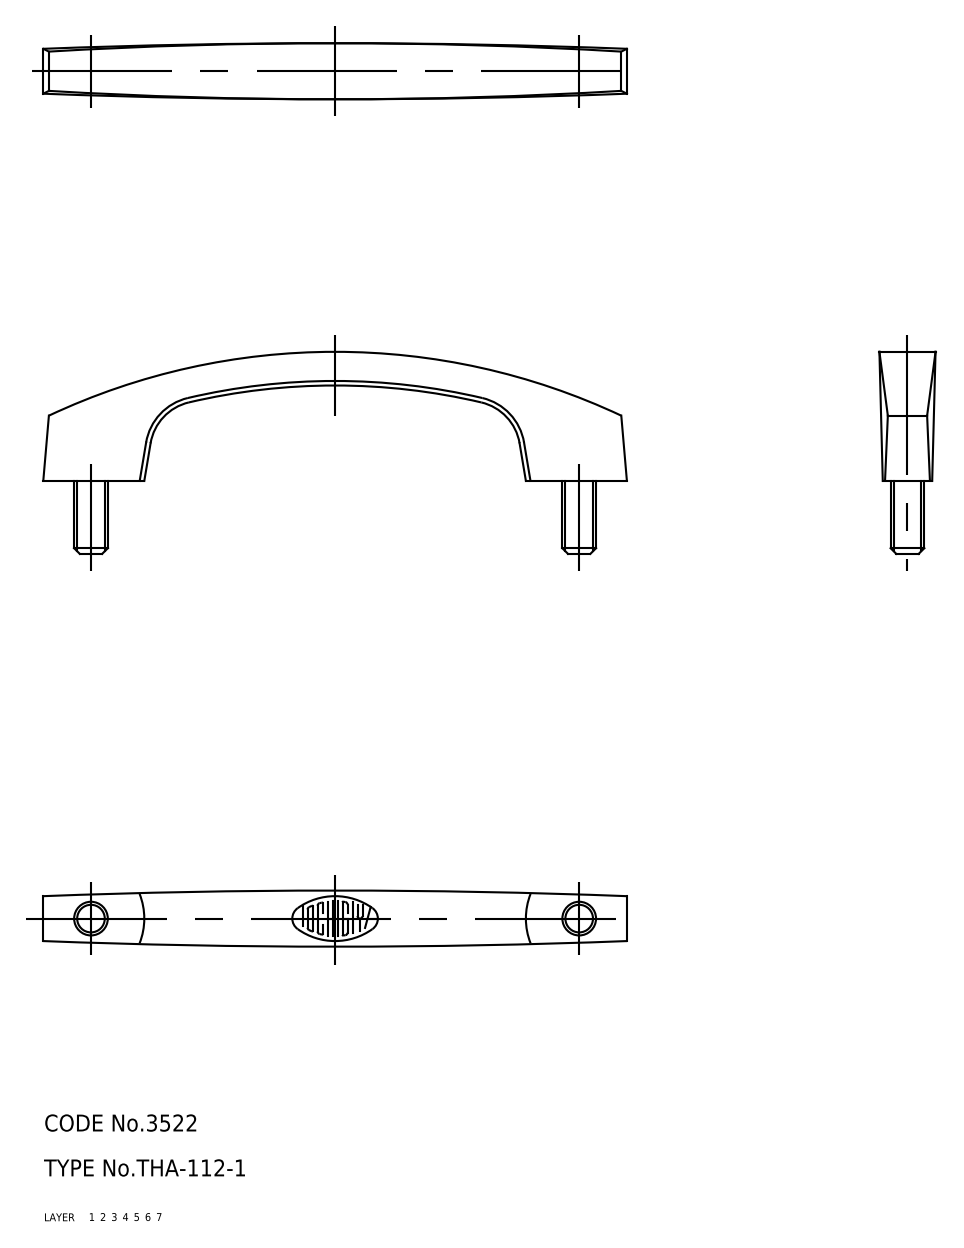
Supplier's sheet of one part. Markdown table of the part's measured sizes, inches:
| quantity | value |
| --- | --- |
| part name | screw; pull; THA_112_1_26643_36 |
| STEP written by | CADfix (AUTOMOTIVE_DESIGN) |
| units | inches |
| bodies | 3 solids, 30 faces (0 planar, 0 cylindrical, 30 other) |
| overall size | 4.094 × 1.417 × 0.394 |
| volume | 0.548 in³ |
| surface area | 8.089 in² |
